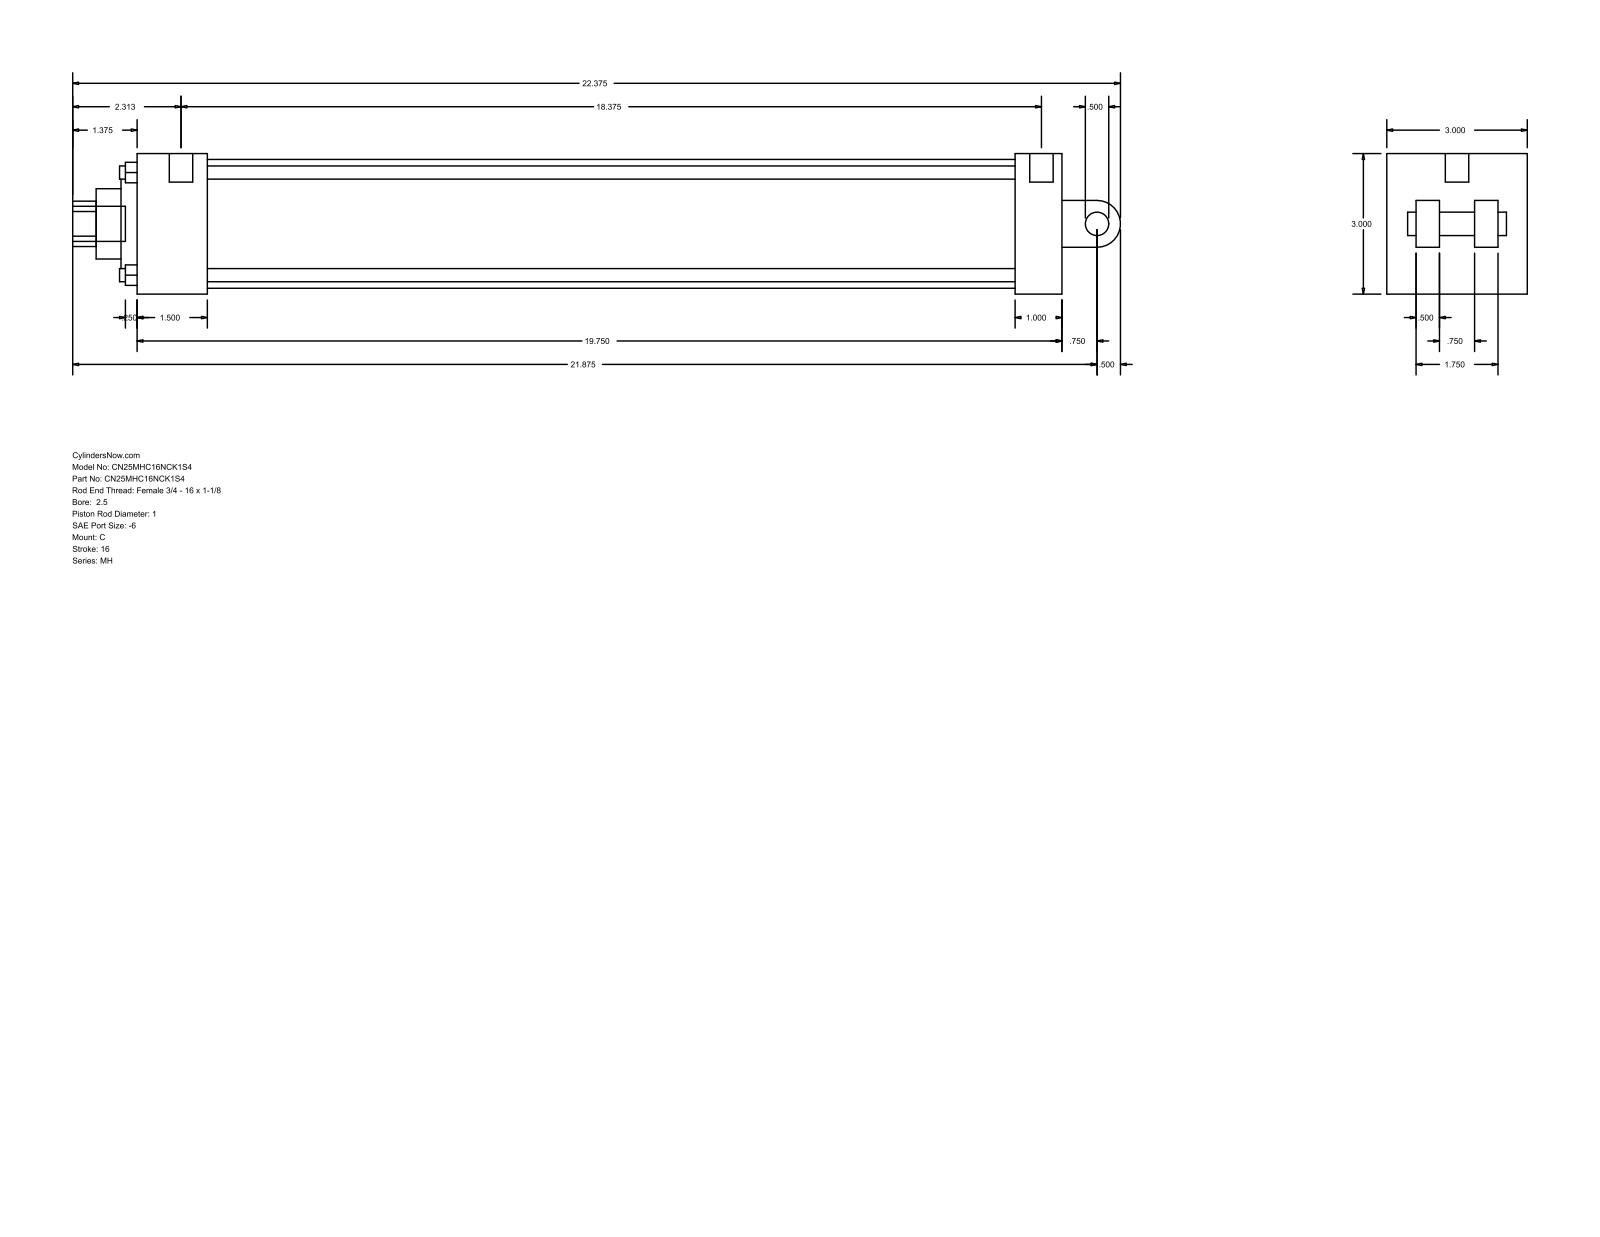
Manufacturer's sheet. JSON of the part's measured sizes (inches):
{"part_name": "MH_C__0250_1", "step_written_by": "GSSL Pune (CONFIG_CONTROL_DESIGN)", "units": "inches", "bodies": {"solids": 0, "faces": 101, "planar": 71, "cylindrical": 30, "other": 0}, "overall_size": [22.375, 3, 3], "round_holes": [[0.281, 4], [0.219, 2], [0.5, 1], [1, 1], [1.5, 1], [2.375, 1], [2.75, 1]], "round_bosses_or_shafts": [[0.5, 2], [0.219, 2], [0.75, 1]], "partial_cylinders_radius": [[0.484, 1], [0.5, 1]], "face_to_face_distances": [3, 1, 19.75, 0.625, 2.375, 18.75, 1.5, 17.25, 18.25, 0.5], "hole_center_spacings": [1.548, 2.19, 3.097, 0.125]}
